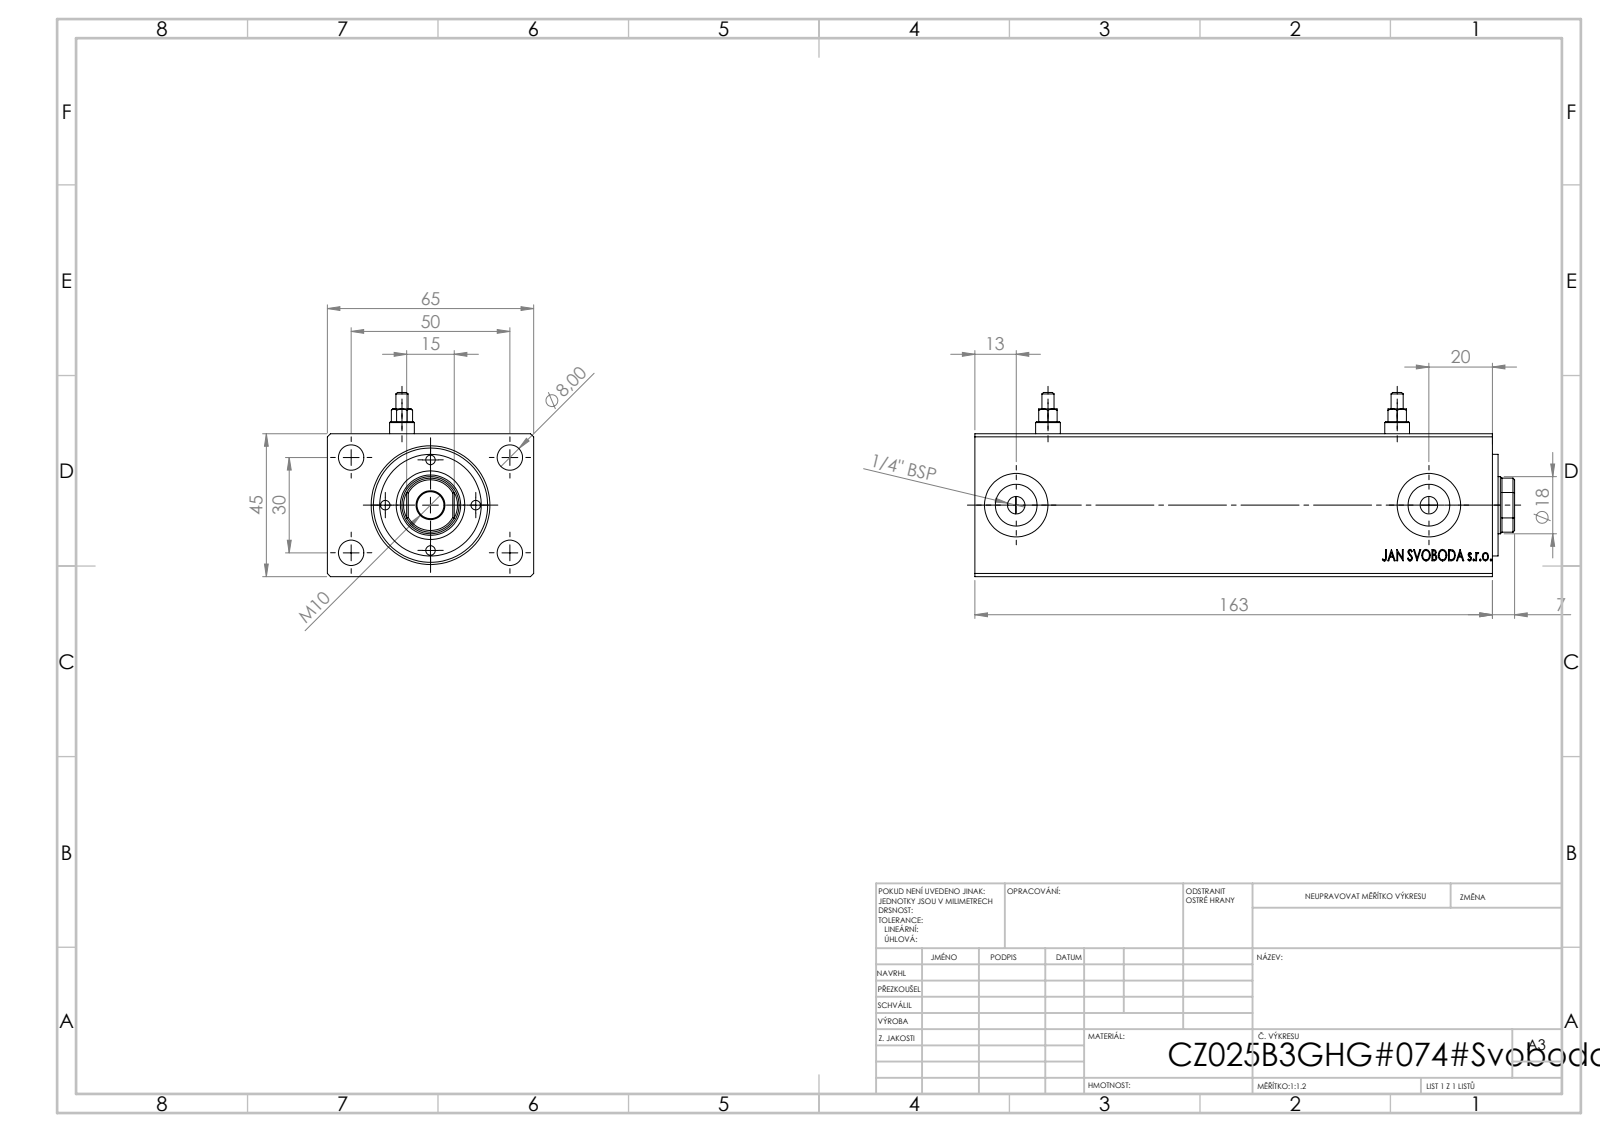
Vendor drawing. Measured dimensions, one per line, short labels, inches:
name: V500CZ_B_VC; V500CZ; Zatka_Cushioning3
written by: SolidWorks 2019 (CONFIG_CONTROL_DESIGN)
unit: in
bodies: 5 solids, 933 faces (423 planar, 74 cylindrical, 436 other)
size: 6.693 × 2.559 × 2.283
volume: 27.18 in³; area: 116.2 in²
holes: 6× ⌀0.315, 4× ⌀0.118, 2× ⌀0.071, 2× ⌀0.217, 2× ⌀0.518, 2× ⌀0.787, 1× ⌀0.335, 1× ⌀0.709, 1× ⌀0.748, 1× ⌀0.984, 1× ⌀1.417
bosses: 2× ⌀0.307, 2× ⌀0.15, 1× ⌀1.26
rounds: 1× R0.335
face distances: 1.772, 2.559, 6.417, 0.276, 6.409, 0.504, 5.913, 0.496, 0.071, 0.205
hole spacings: 0.561, 0.726, 0.793, 0.985, 1.148, 1.515, 1.654, 1.122
